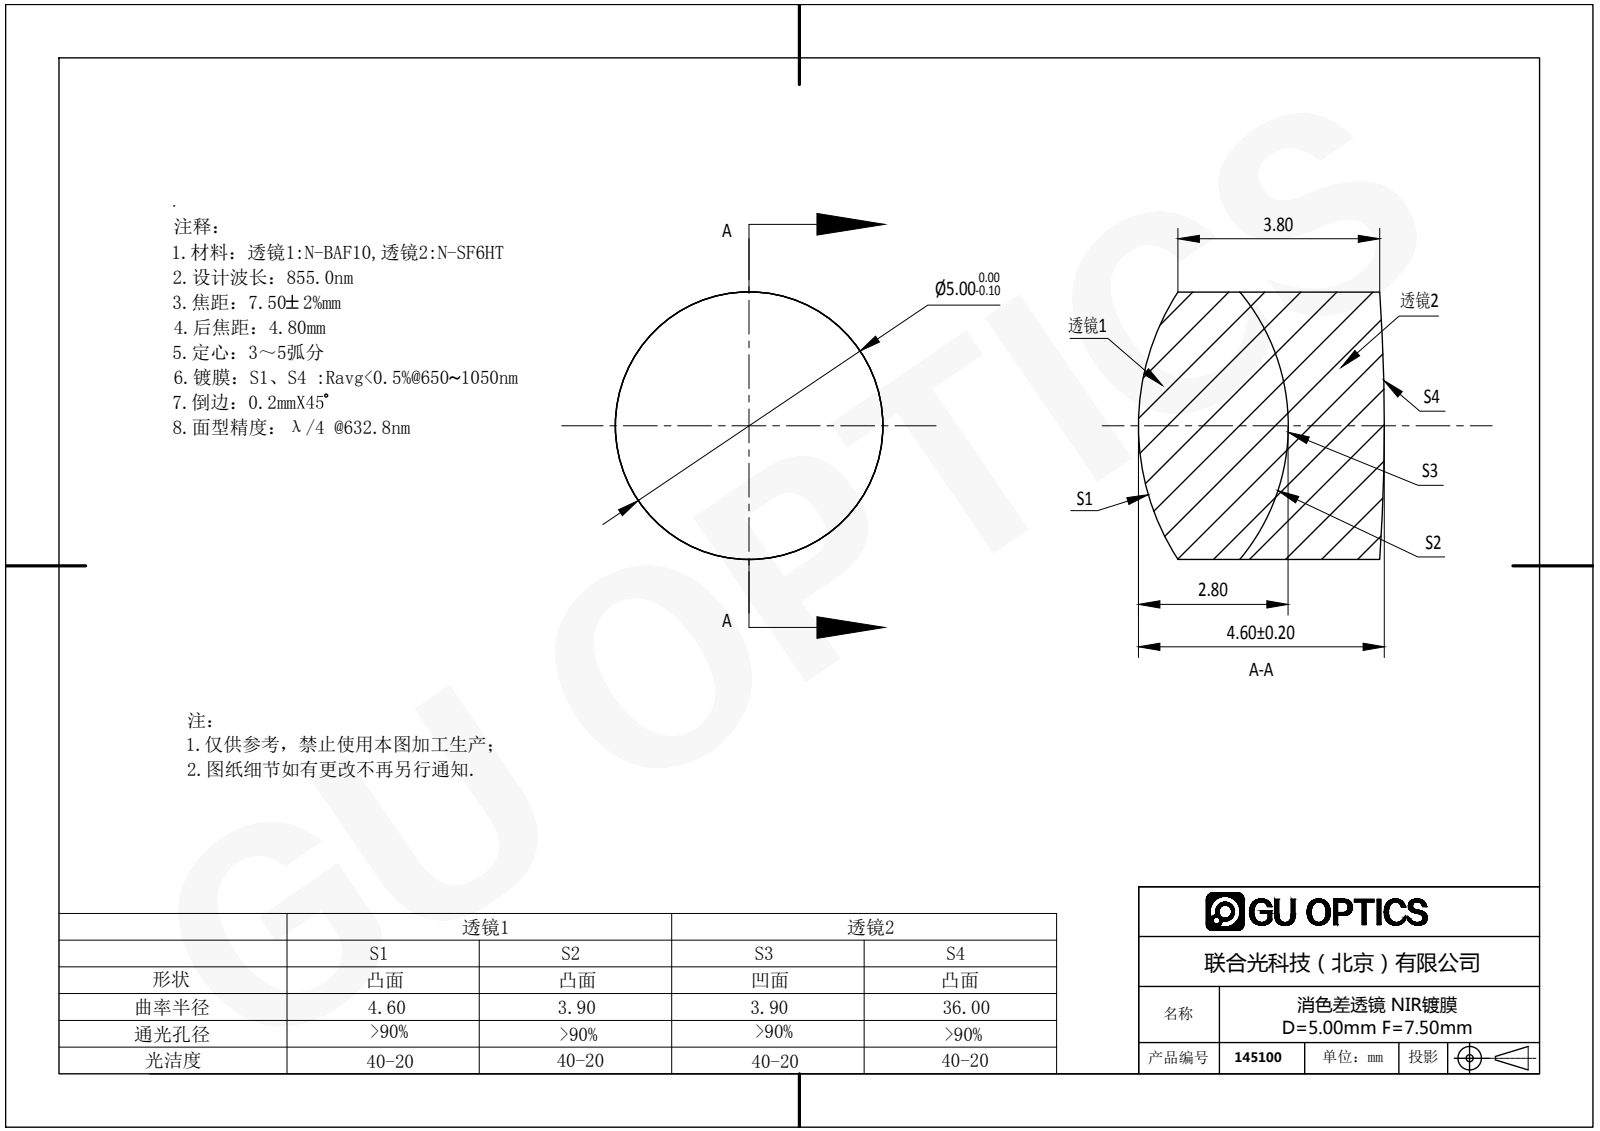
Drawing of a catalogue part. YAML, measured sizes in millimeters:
part_name: "145100"
step_written_by: "SolidWorks 2016 (AUTOMOTIVE_DESIGN)"
units: millimeters
bodies: {solids: 2, faces: 12, planar: 0, cylindrical: 4, other: 8}
overall_size: [5, 5, 4.6]
volume: 82
surface_area: 145
round_bosses_or_shafts:
  - {diameter: 5, count: 1}
